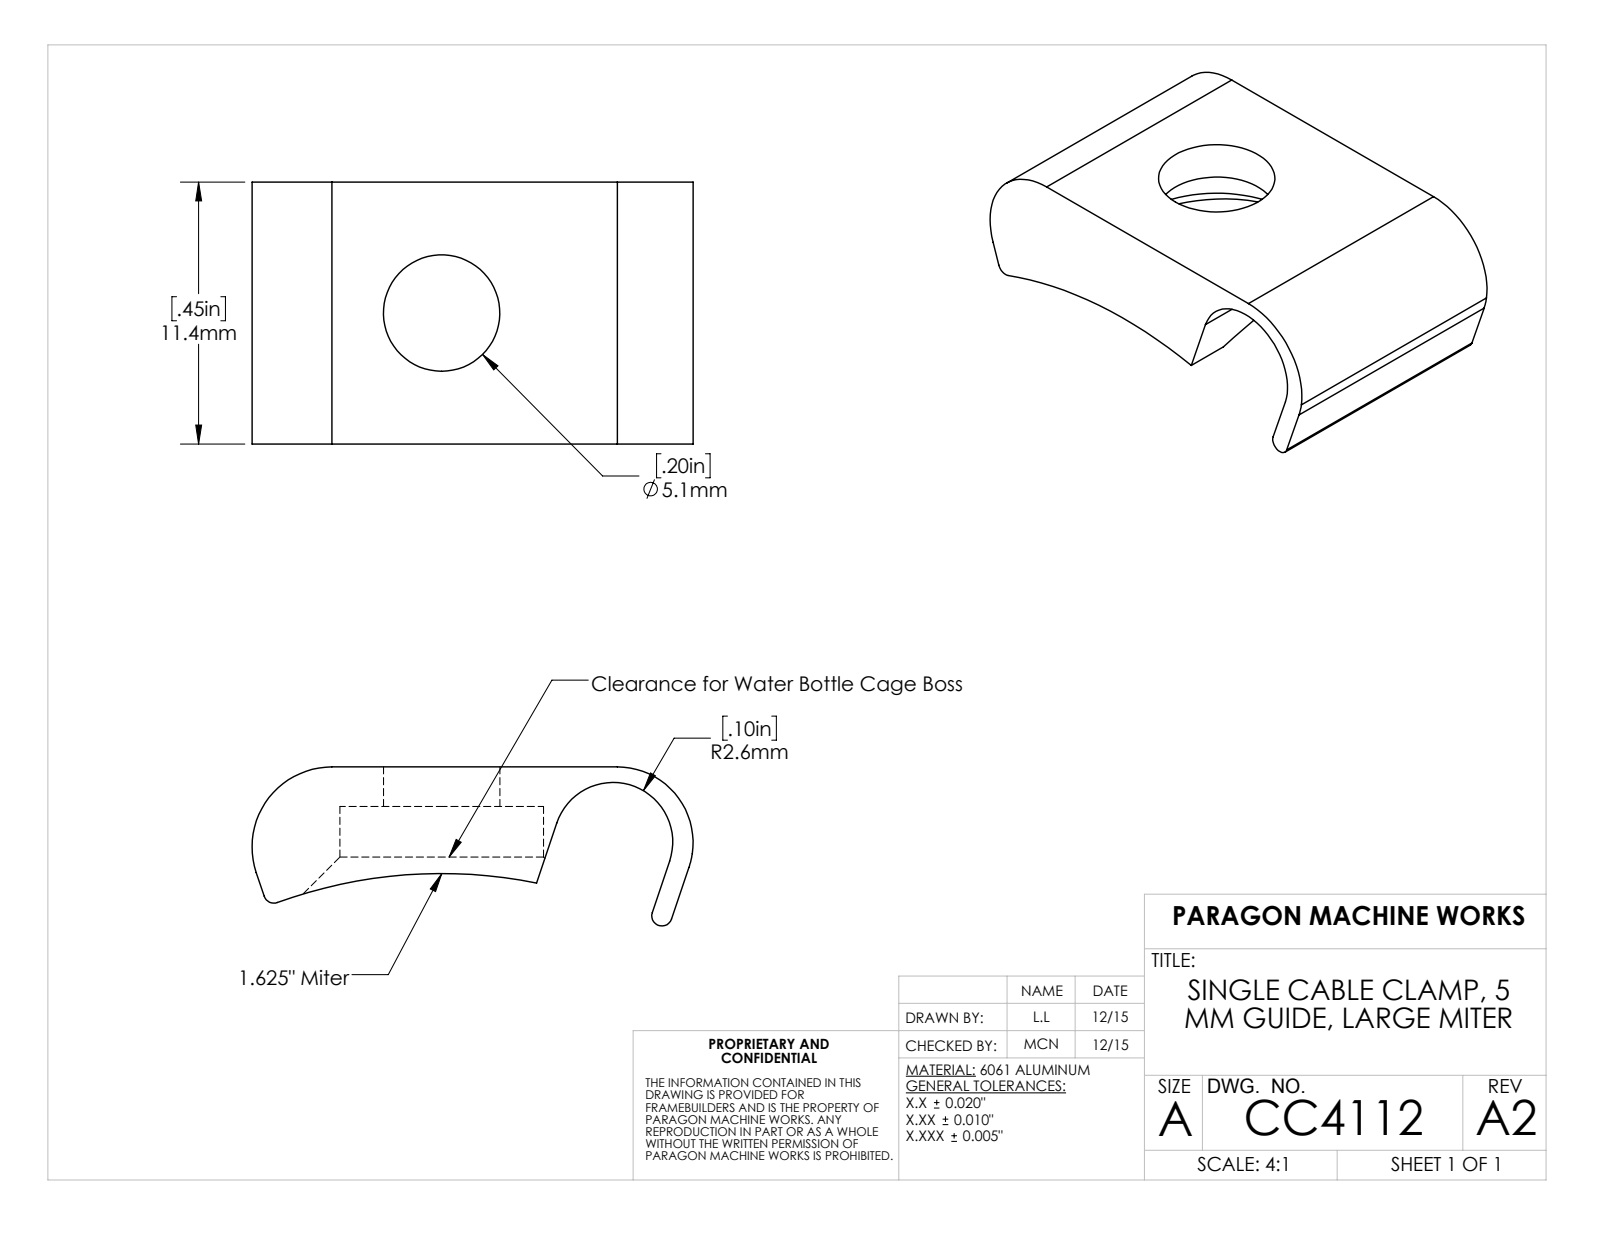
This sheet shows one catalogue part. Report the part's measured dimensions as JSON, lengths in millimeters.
{"part_name": "CC4112", "step_written_by": "SolidWorks 2015 (AUTOMOTIVE_DESIGN)", "units": "millimeters", "bodies": {"solids": 1, "faces": 23, "planar": 8, "cylindrical": 13, "other": 2}, "overall_size": [19.3, 11.4, 6.9], "volume_mm3": 590, "surface_area_mm2": 838, "round_holes": [[5.1, 1], [8.9, 1]], "partial_cylinders_radius": [[3.5, 2], [0.4, 1], [0.5, 1], [2.6, 1], [3.3, 1], [20.9, 1]], "face_to_face_distances": [11.4, 1.7, 0.9, 5.2, 6.1]}
